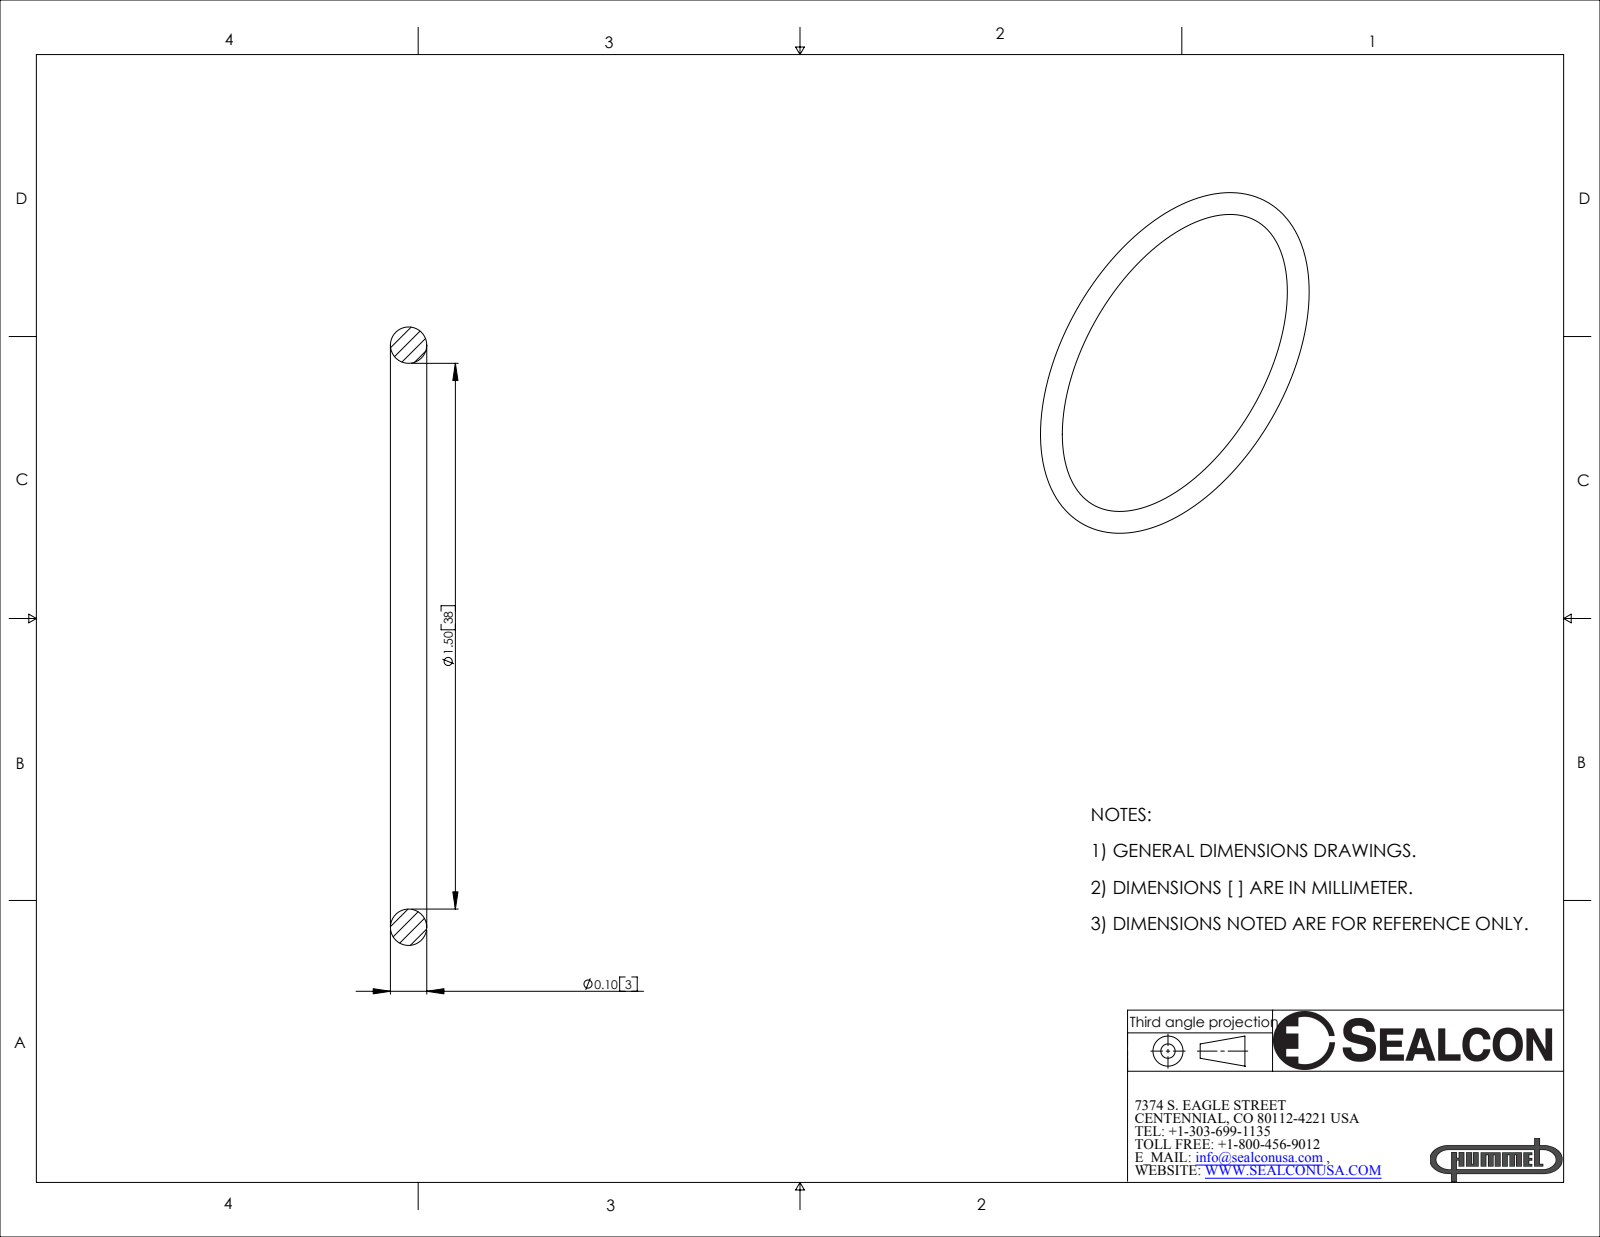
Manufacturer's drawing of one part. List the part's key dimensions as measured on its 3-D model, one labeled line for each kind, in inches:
Part name (STEP PRODUCT): OR-54-BN
STEP written by: SolidWorks 2007 (CONFIG_CONTROL_DESIGN)
Units: inches
Bodies: 1 solid, 4 faces (0 planar, 0 cylindrical, 4 other)
Overall size (bounding box): 1.7 × 1.7 × 0.1
Volume: 0.039 in³ · Surface area: 1.579 in²
